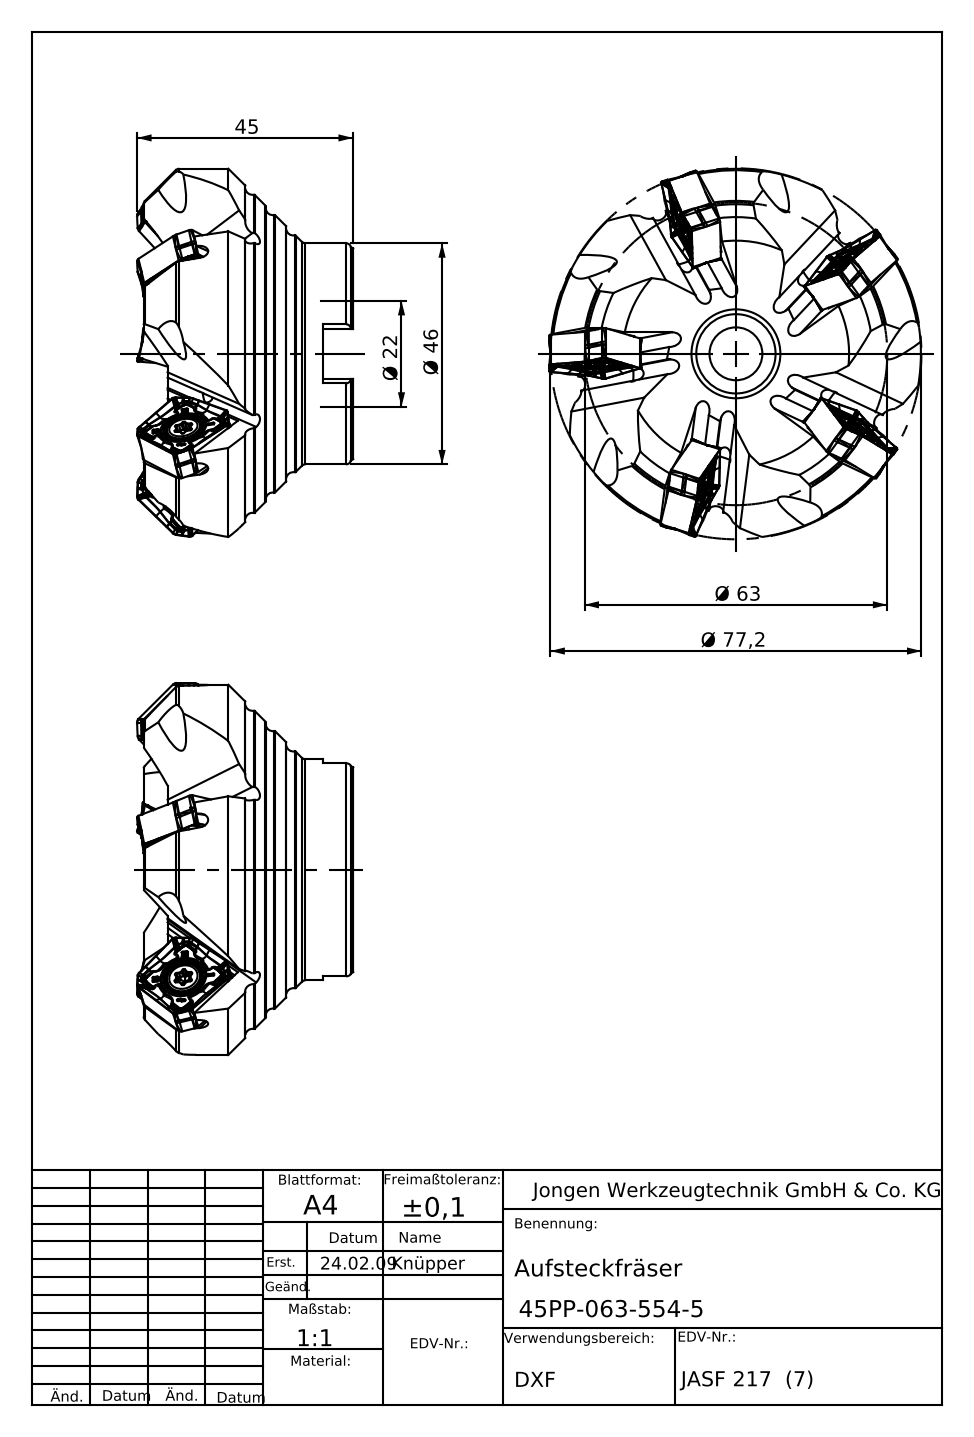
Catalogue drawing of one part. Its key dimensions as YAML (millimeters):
part_name: "45PP-063-554-5"
step_written_by: "SolidWorks 2012 (AUTOMOTIVE_DESIGN)"
units: millimeters
bodies: {solids: 1, faces: 276, planar: 105, cylindrical: 71, other: 100}
overall_size: [78.3, 78.3, 45]
volume: 114424
surface_area: 22945
round_holes:
  - {diameter: 3, count: 5}
  - {diameter: 11, count: 1}
  - {diameter: 16.5, count: 1}
  - {diameter: 22, count: 1}
  - {diameter: 22.15, count: 1}
  - {diameter: 22.3, count: 1}
round_bosses_or_shafts:
  - {diameter: 78.3, count: 1}
  - {diameter: 46, count: 1}
partial_cylinders:
  - {radius: 1.5, count: 15}
  - {radius: 1.5, count: 5}
  - {radius: 1.65, count: 5}
  - {radius: 38.5, count: 1}
face_to_face_distances: [38.65, 45, 6.35, 6.3, 32.35, 38.7, 22, 15.7, 16.65, 23]
